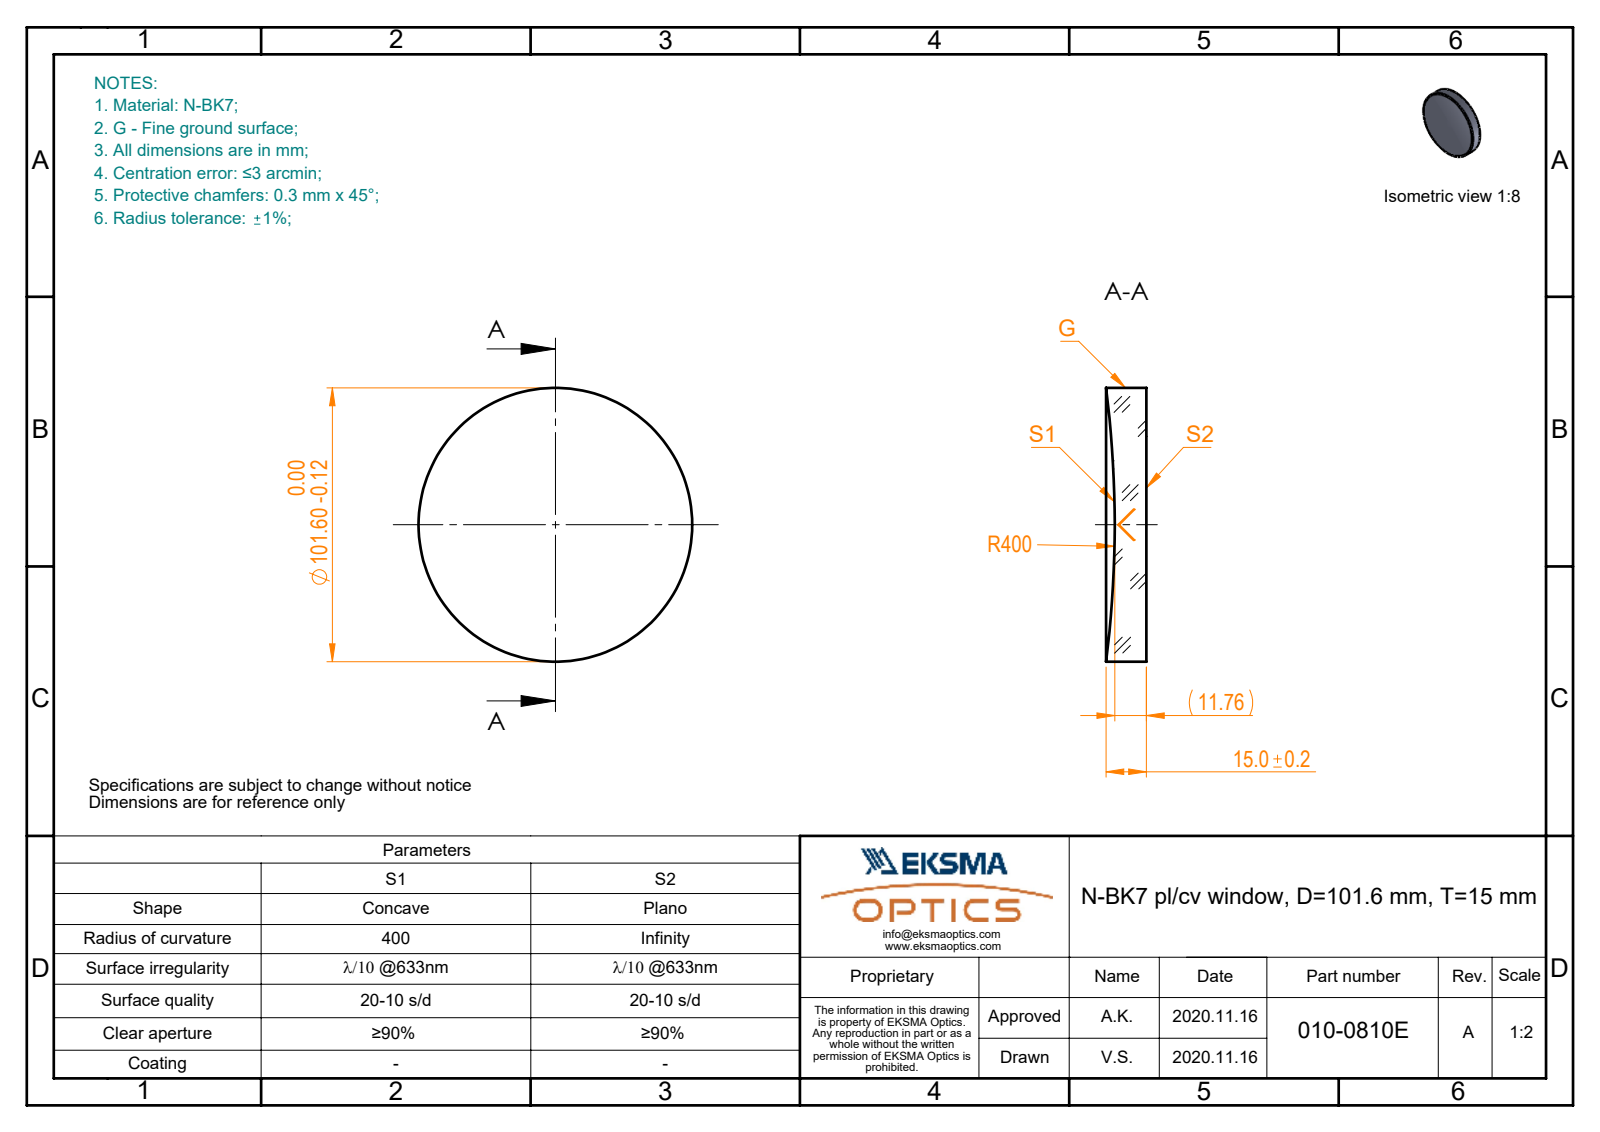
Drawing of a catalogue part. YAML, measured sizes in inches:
part_name: "010-0810E_N-BK7_PCV_window"
step_written_by: "SolidWorks 2019 (CONFIG_CONTROL_DESIGN)"
units: inches
bodies: {solids: 1, faces: 5, planar: 1, cylindrical: 2, other: 2}
overall_size: [4, 4, 0.591]
volume: 6.619
surface_area: 32.6
round_bosses_or_shafts:
  - {diameter: 4, count: 1}
